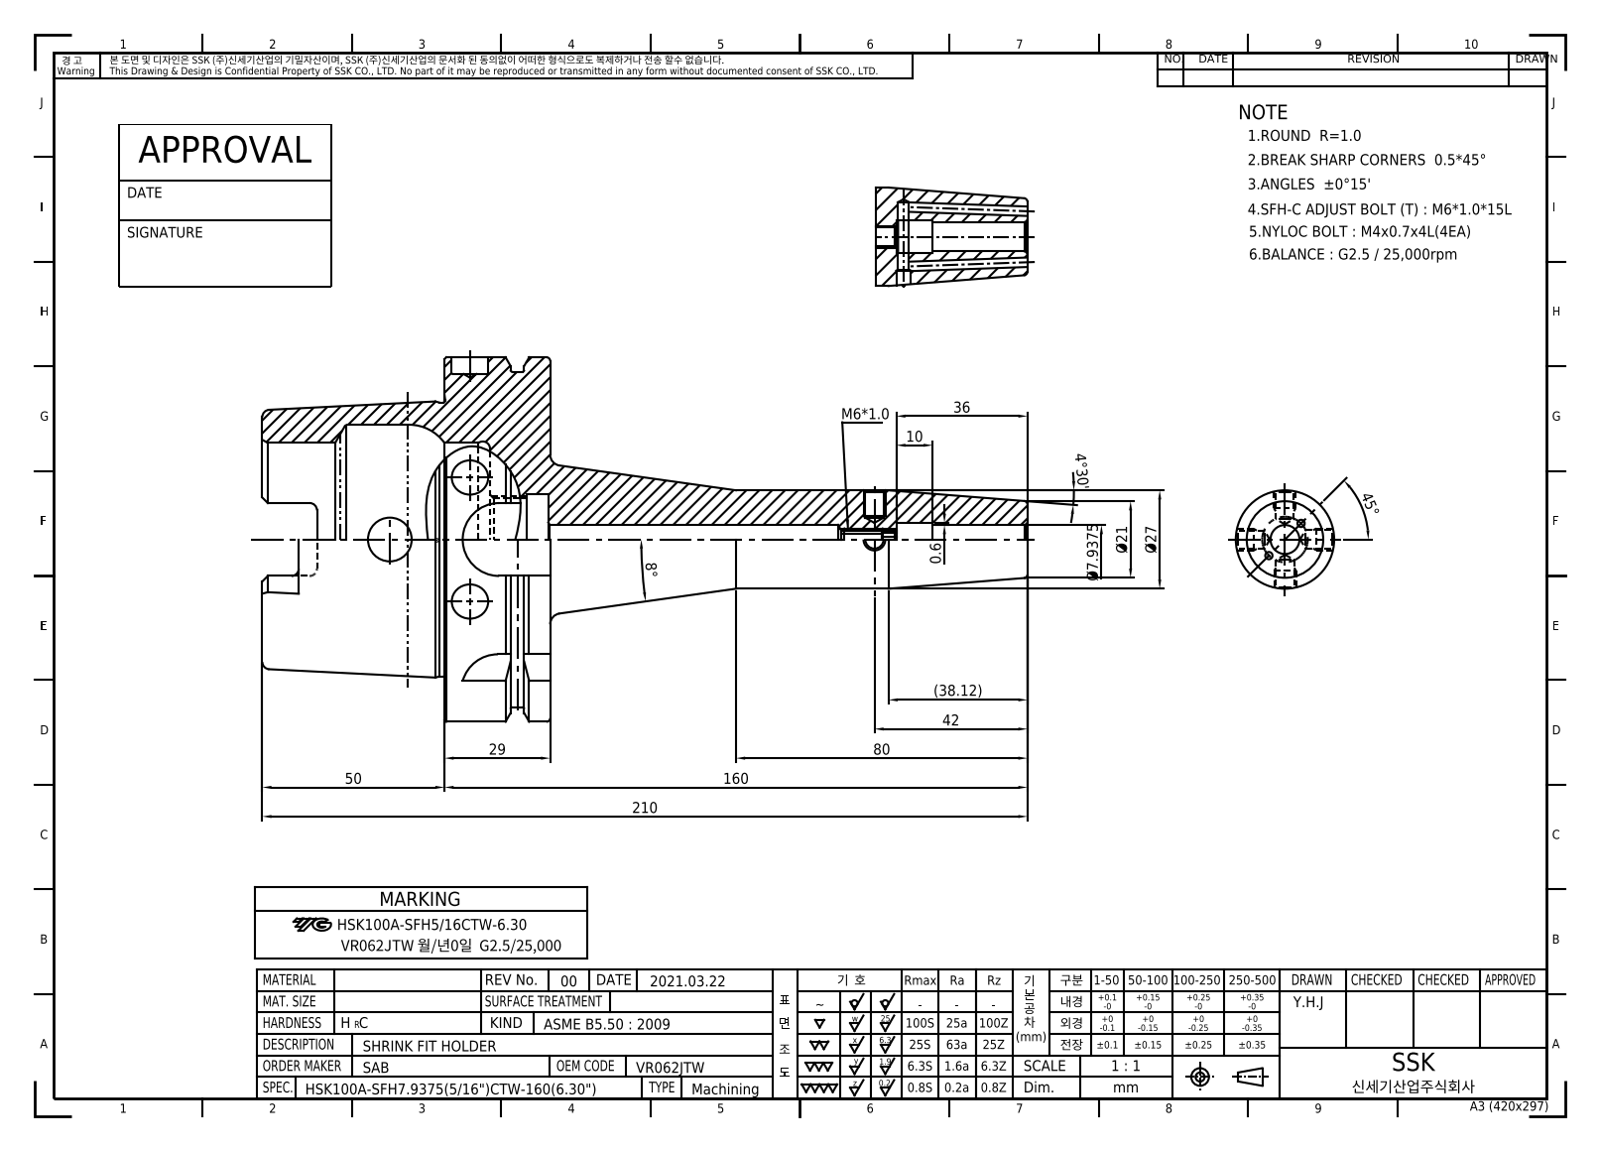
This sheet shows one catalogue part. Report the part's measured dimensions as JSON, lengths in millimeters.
{"part_name": "LO-HSK100A-SFH7.9375CTW-160", "step_written_by": "Autodesk Inventor 2022 (AUTOMOTIVE_DESIGN)", "units": "millimeters", "bodies": {"solids": 1, "faces": 120, "planar": 38, "cylindrical": 37, "other": 45}, "overall_size": [210, 100, 100], "volume_mm3": 331408, "surface_area_mm2": 64120, "round_holes": [[2.5, 2], [4.92, 1], [7.94, 1], [8, 1], [9.14, 1], [10, 1], [12, 1], [22.38, 1], [25, 1], [53, 1], [63, 1]], "round_bosses_or_shafts": [[100, 1], [92, 1], [75.41, 1], [27, 1]], "partial_cylinders_radius": [[2, 6], [4.88, 4], [10, 4]], "face_to_face_distances": [29, 12.5, 16.5, 62.5, 50, 79, 78.5, 28.5, 16, 0.5]}
